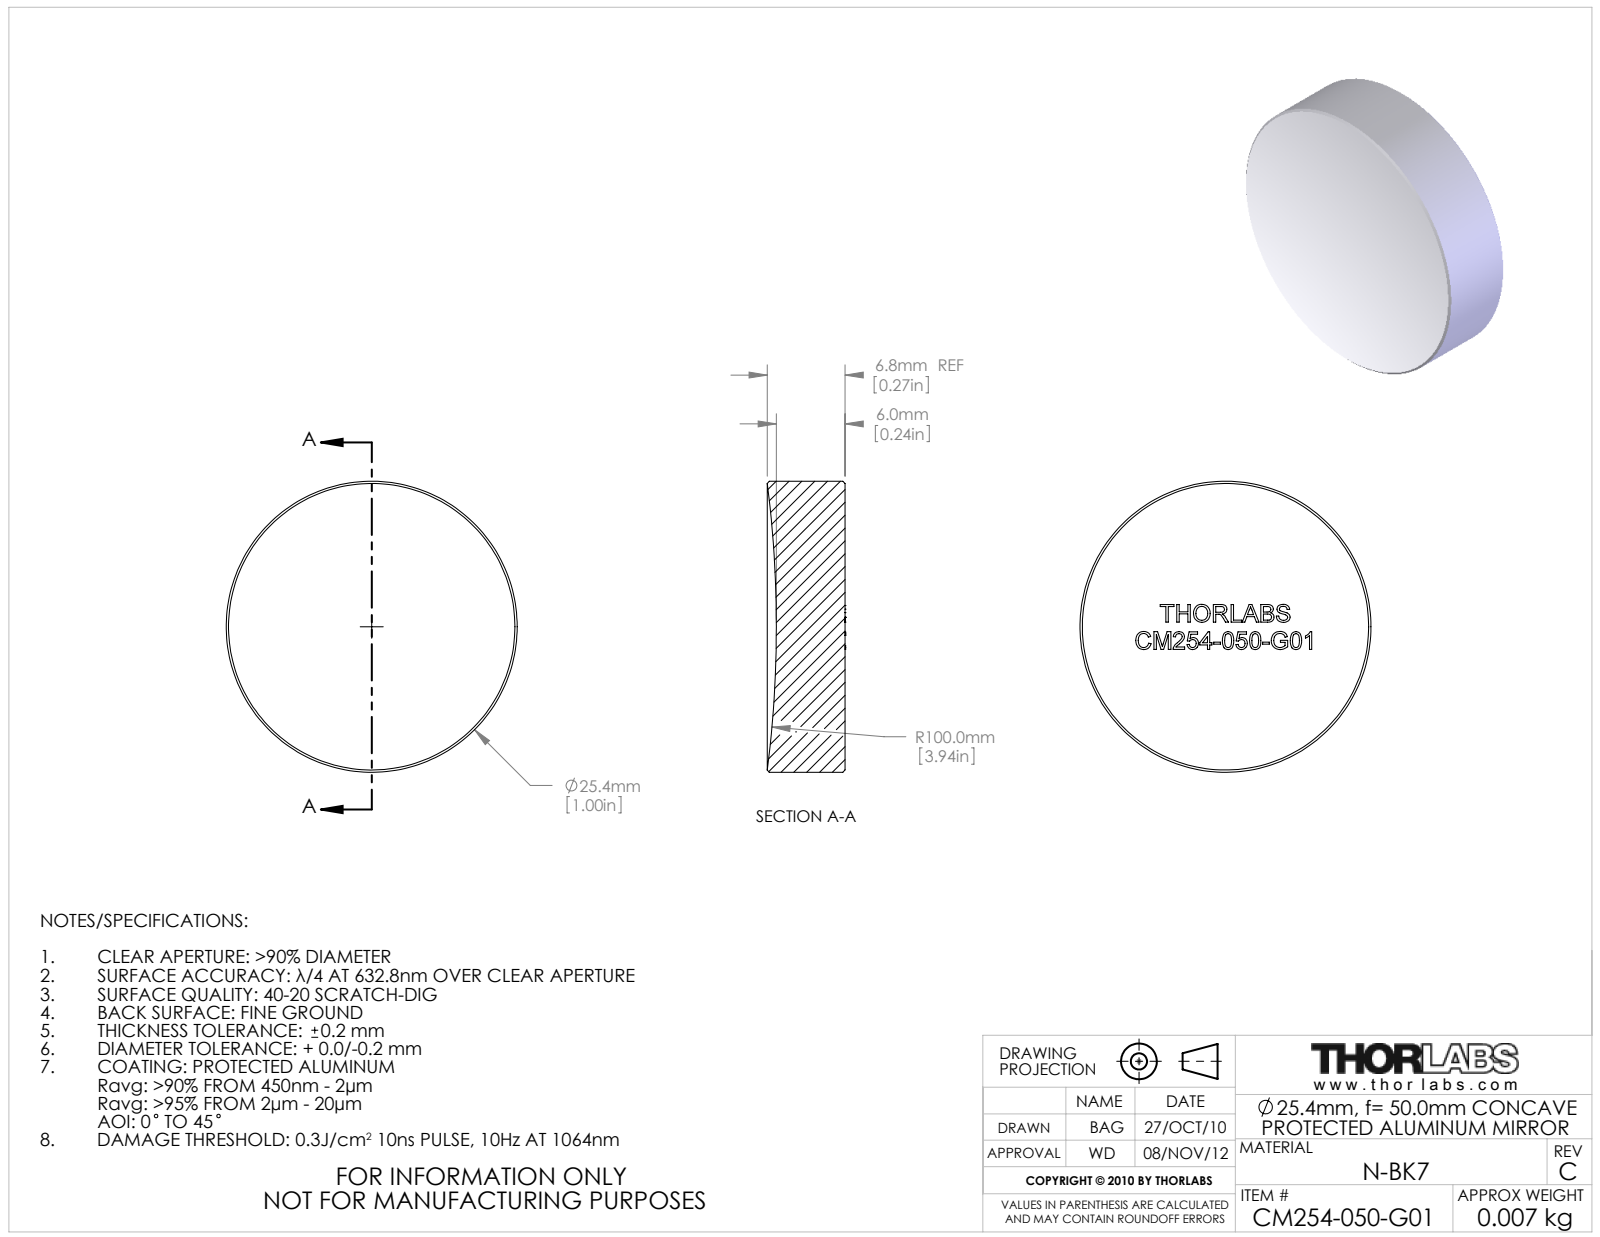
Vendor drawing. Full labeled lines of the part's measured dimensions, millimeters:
Part name (STEP PRODUCT): 12010-E0W
STEP written by: SolidWorks 2009 (AUTOMOTIVE_DESIGN)
Units: millimetres
Bodies: 1 solid, 284 faces (156 planar, 2 cylindrical, 126 other)
Overall size (bounding box): 25.4 × 25.4 × 6.8
Volume: 3 240 mm³ · Surface area: 1 539 mm²
Round bosses / shafts (diameter × count): ⌀25.4 ×1
Main face-to-face distances: 1.9, 1.5, 0.7, 1.7, 4.1, 0.9, 2.4, 3.9, 1.3, 3.2
